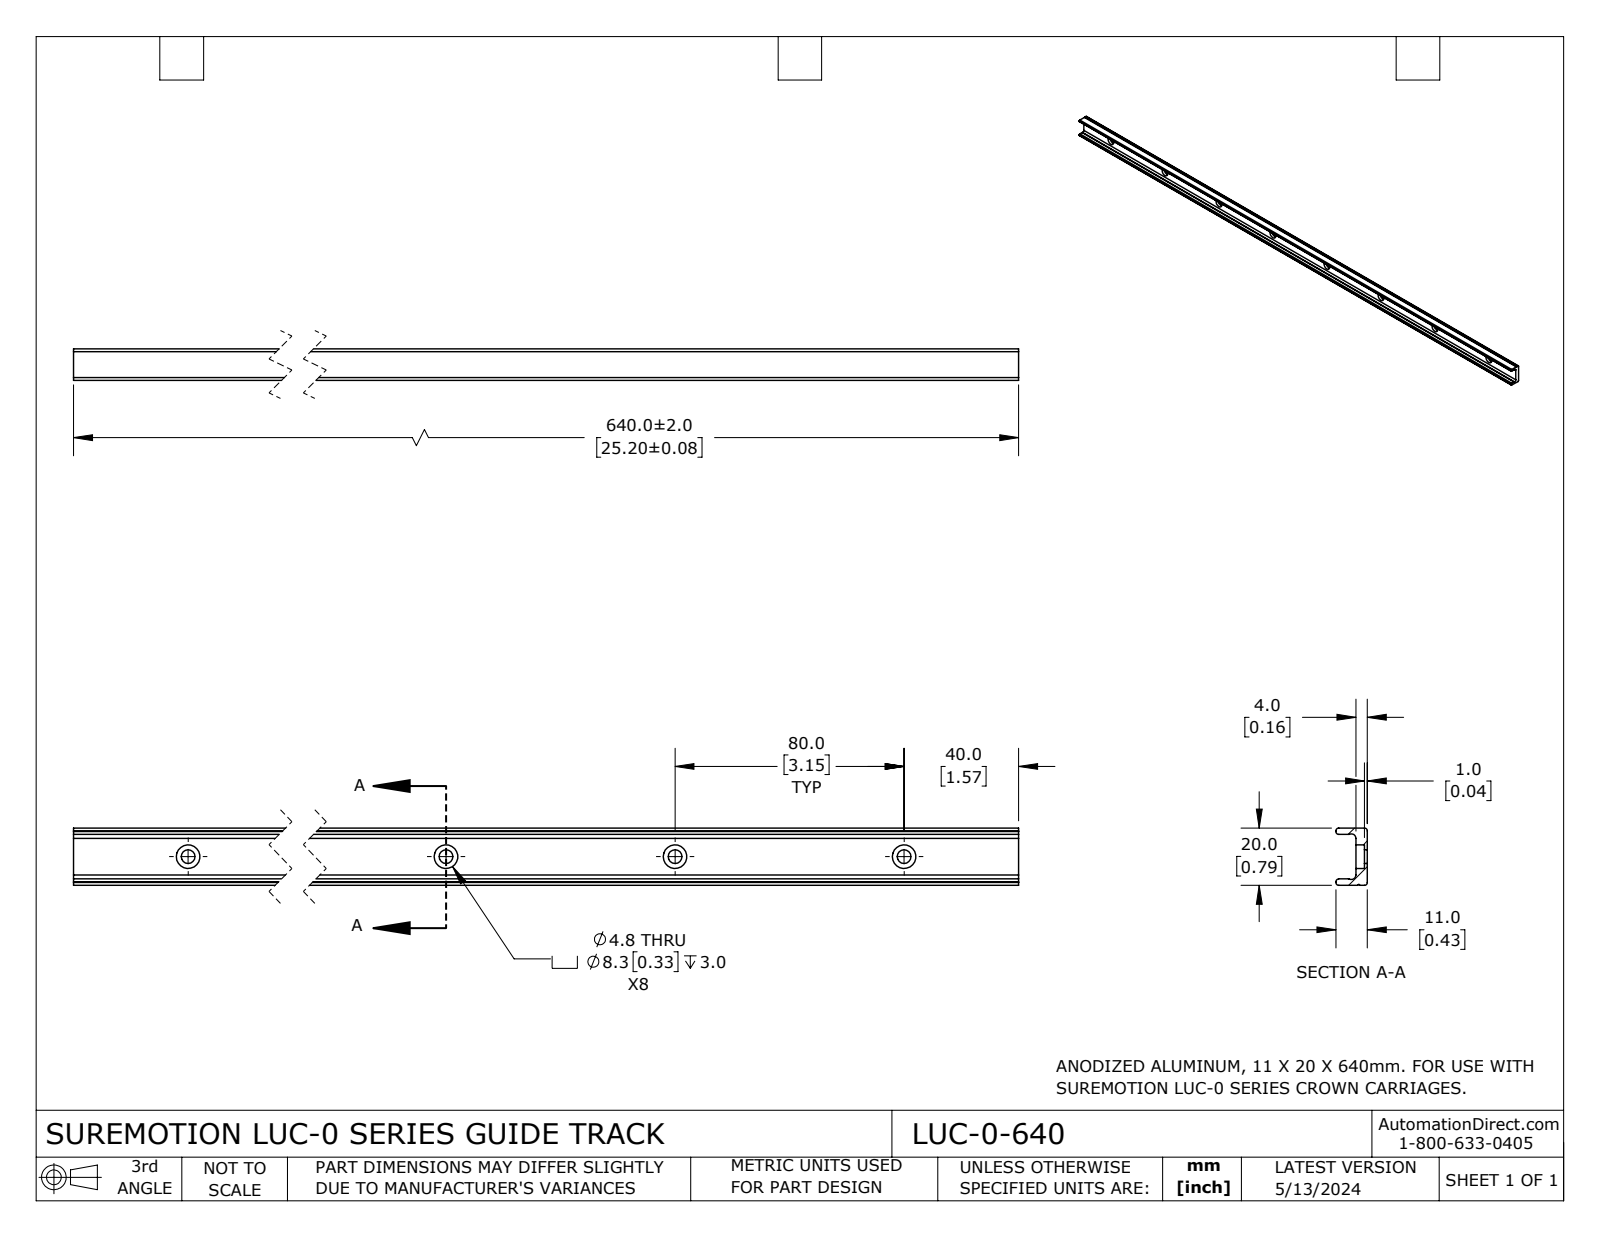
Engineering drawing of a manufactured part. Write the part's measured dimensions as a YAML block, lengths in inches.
part_name: "LUC-0-640"
step_written_by: "SolidWorks 2023 (CONFIG_CONTROL_DESIGN)"
units: inches
bodies: {solids: 1, faces: 62, planar: 19, cylindrical: 43, other: 0}
overall_size: [25.197, 0.787, 0.433]
volume: 4.213
surface_area: 73.32
round_holes:
  - {diameter: 0.189, count: 8}
  - {diameter: 0.325, count: 5}
  - {diameter: 0.325, count: 3}
partial_cylinders:
  - {radius: 0.039, count: 8}
  - {radius: 0.063, count: 2}
  - {radius: 0.013, count: 1}
face_to_face_distances: [0.158, 0.787, 0.088, 0.7, 0.612, 0.433, 0.275, 0.04, 0.118, 0.393]
hole_center_spacings: [3.15, 6.299, 9.449, 12.598, 15.748, 18.898, 22.047]
